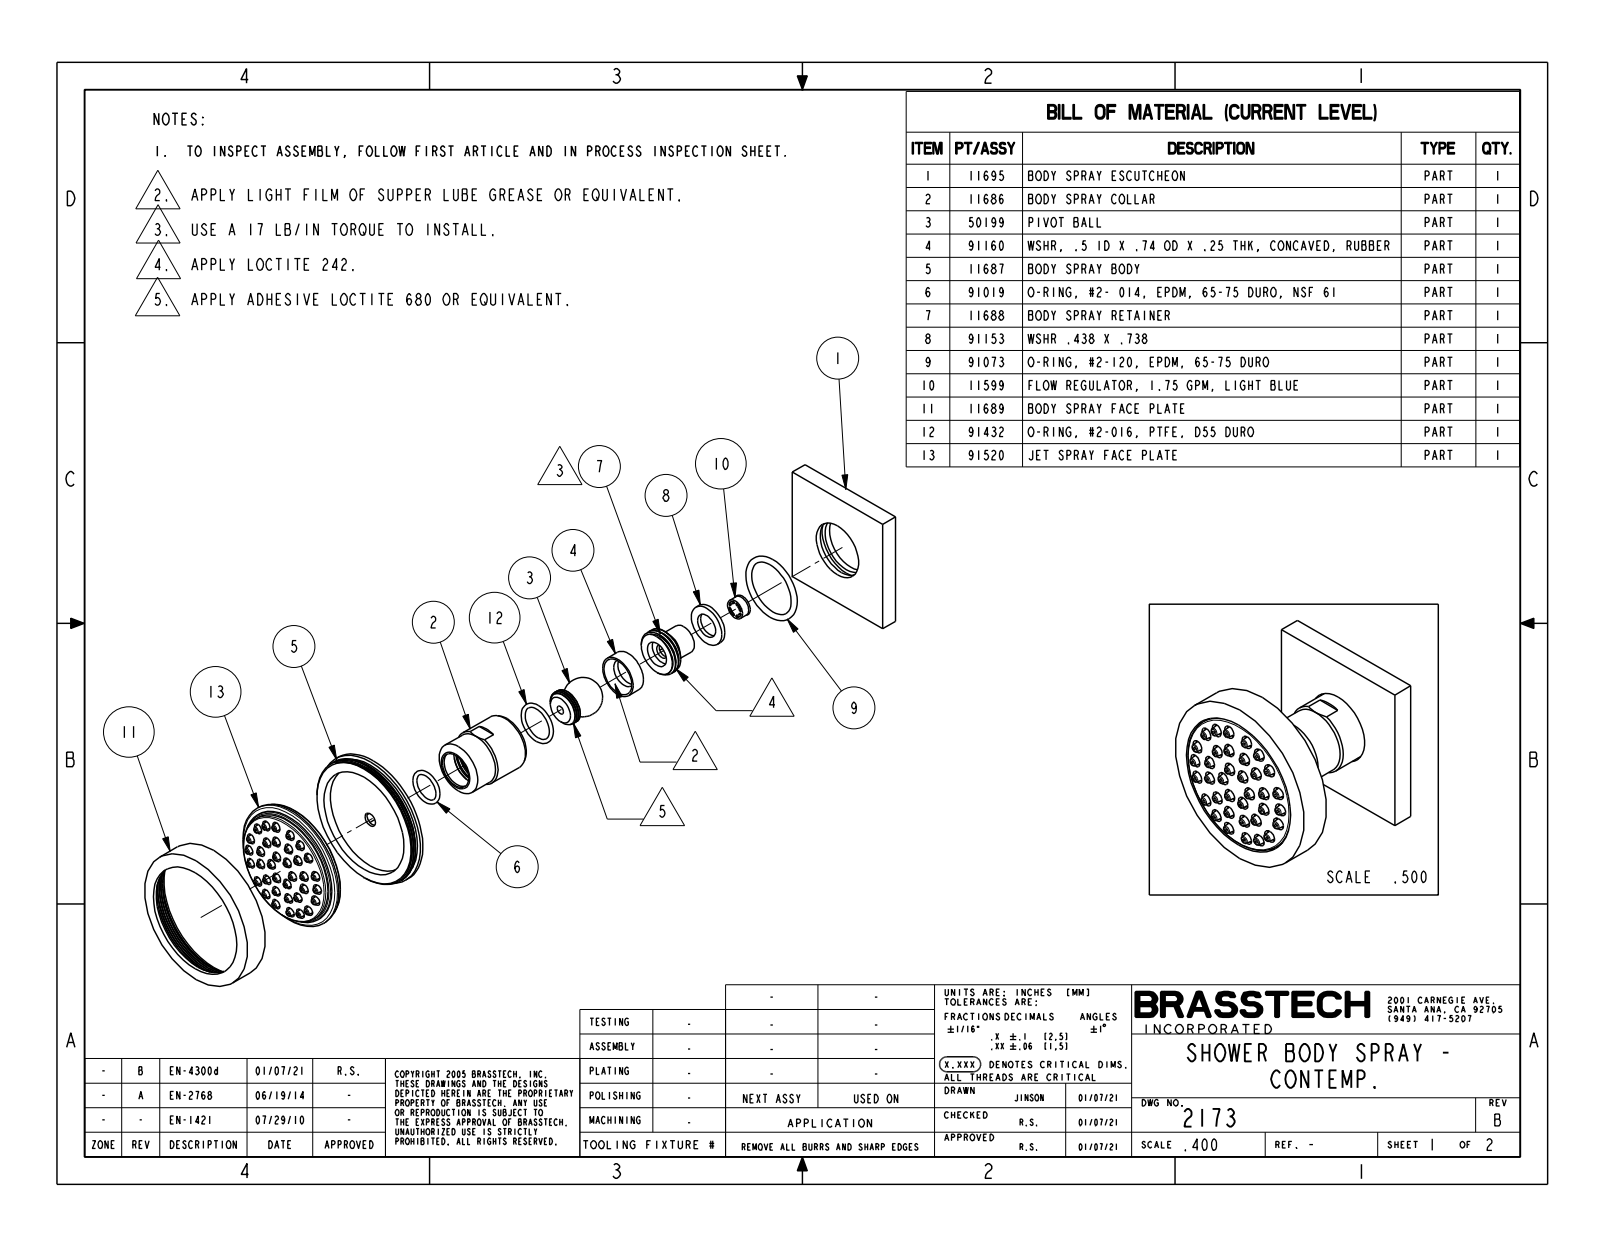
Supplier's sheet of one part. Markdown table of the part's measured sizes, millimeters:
| quantity | value |
| --- | --- |
| part name | 2173 |
| STEP written by | CREO PARAMETRIC BY PTC INC, 2018400 (CONFIG_CONTROL_DESIGN) |
| units | millimeters |
| bodies | 1 solid, 441 faces (50 planar, 153 cylindrical, 238 other) |
| overall size | 63.5 × 63.5 × 59.5 |
| volume | 76 770 mm³ |
| surface area | 21 500 mm² |
| round holes (diameter × count) | 1 × 36, 4.6 × 31, 51.4 × 1 |
| round bosses / shafts (diameter × count) | 63.5 × 1, 50.6 × 1, 25.4 × 1, 23.8 × 1, 22 × 1, 8 × 1 |
| partial cylindrical surfaces (radius × count) | 2.3 × 5 |
| main face-to-face distances | 45.3, 7.9, 37.4, 55.9, 35.3, 27.4, 10, 16, 39.9, 31.5 |
| hole center spacings | 21, 36.4, 13.7, 15.1, 32.6, 39.2, 26.4, 28.1 |
